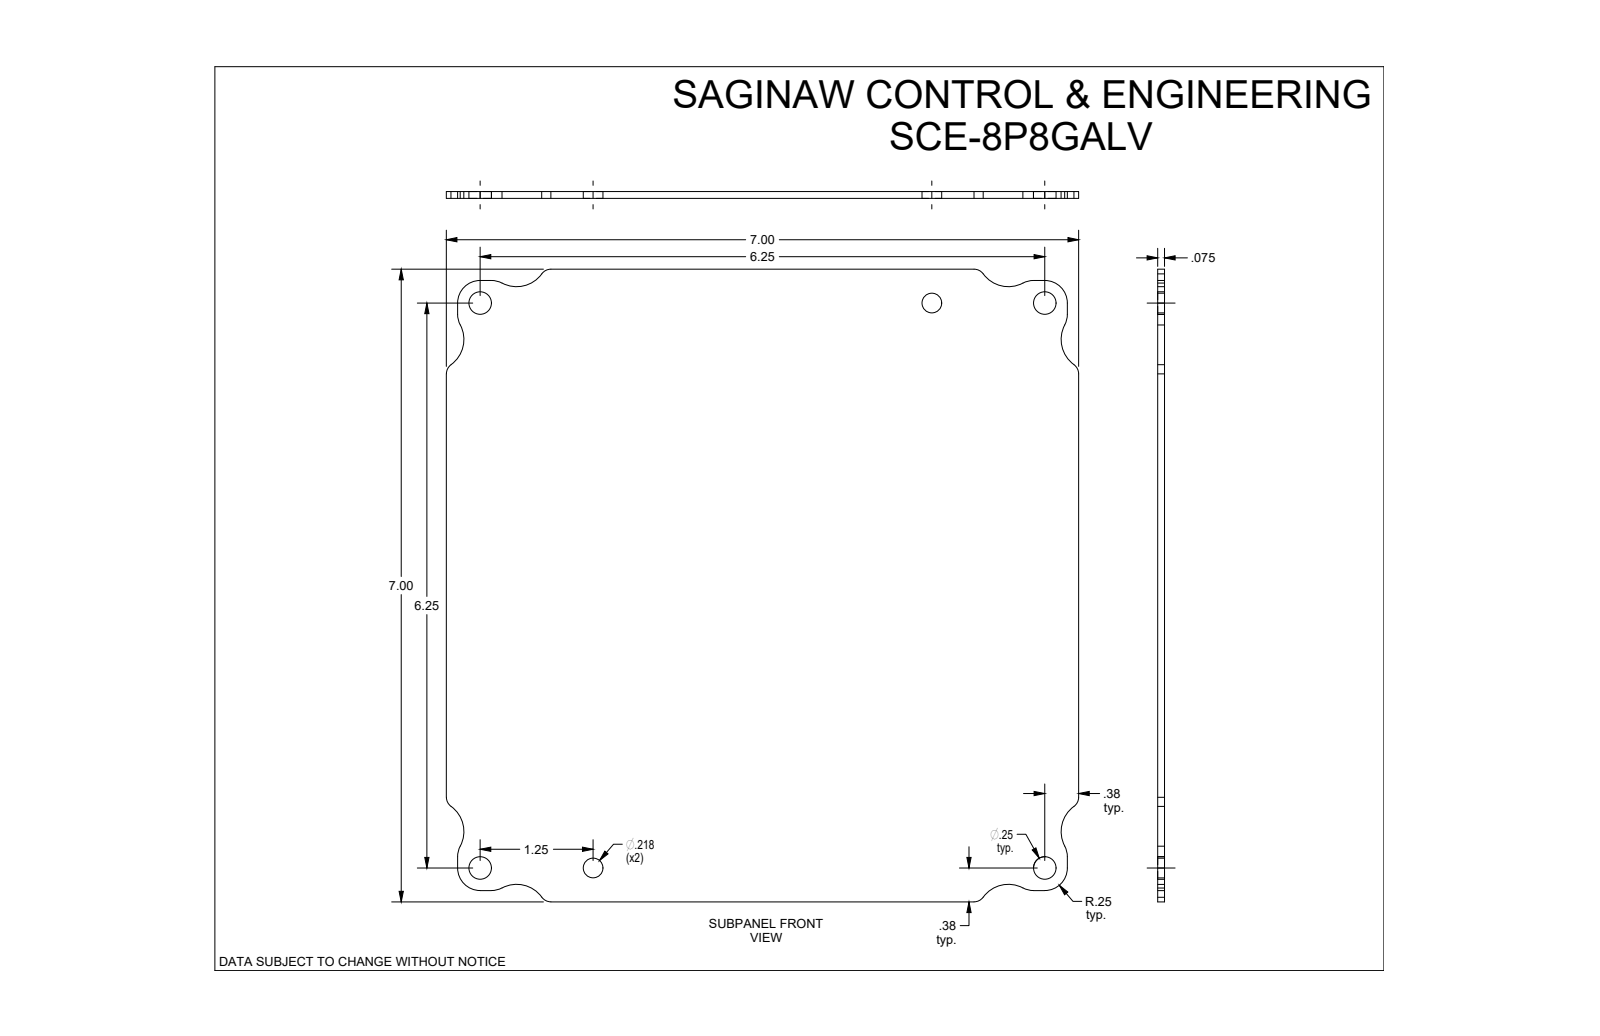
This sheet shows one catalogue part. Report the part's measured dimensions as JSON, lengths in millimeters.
{"part_name": "SCE-8P8GALV", "step_written_by": "SolidWorks 2019 (CONFIG_CONTROL_DESIGN)", "units": "millimeters", "bodies": {"solids": 1, "faces": 48, "planar": 14, "cylindrical": 34, "other": 0}, "overall_size": [177.8, 177.8, 1.9], "volume_mm3": 58420, "surface_area_mm2": 62860, "round_holes": [[6.4, 4], [5.5, 2]], "partial_cylinders_radius": [[6.4, 12], [3.2, 8], [8.7, 8]], "face_to_face_distances": [1.9, 177.8, 3.2, 174.6, 171.5], "hole_center_spacings": [158.8, 31.8, 127, 161.9, 203.3, 224.5, 185.1]}
